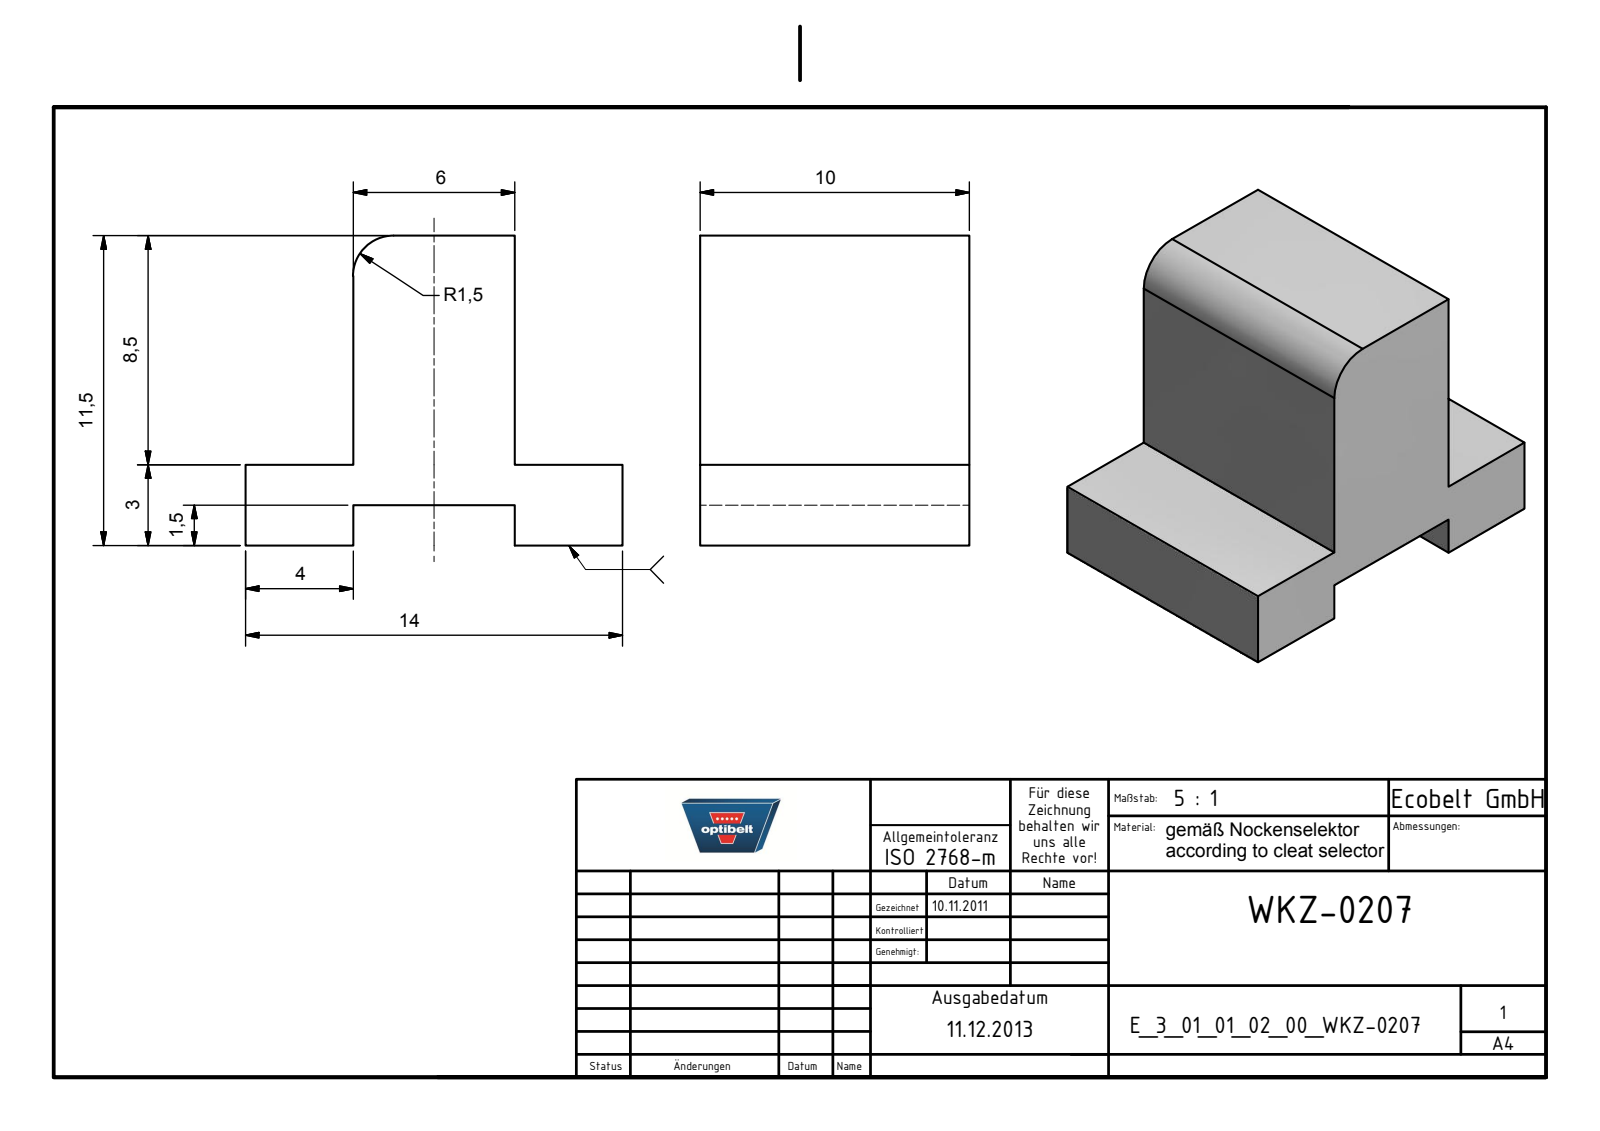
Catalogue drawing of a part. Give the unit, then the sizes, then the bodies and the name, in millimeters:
Units: millimetres
Overall size (bounding box): 14 × 11.5 × 10
Partial cylindrical surfaces — rounded edges, fillets, slot ends (radius × count): R1.5 ×1
Main face-to-face distances: 10, 1.5, 6, 3, 4, 11.5, 8.5, 14
Volume: 835 mm³ · Surface area: 701 mm²
Bodies: 1 solid, 15 faces (14 planar, 1 cylindrical, 0 other)
Part name (STEP PRODUCT): E_3_01_01_02_00_WKZ-0207
STEP written by: Autodesk Inventor 2021 (AUTOMOTIVE_DESIGN)
